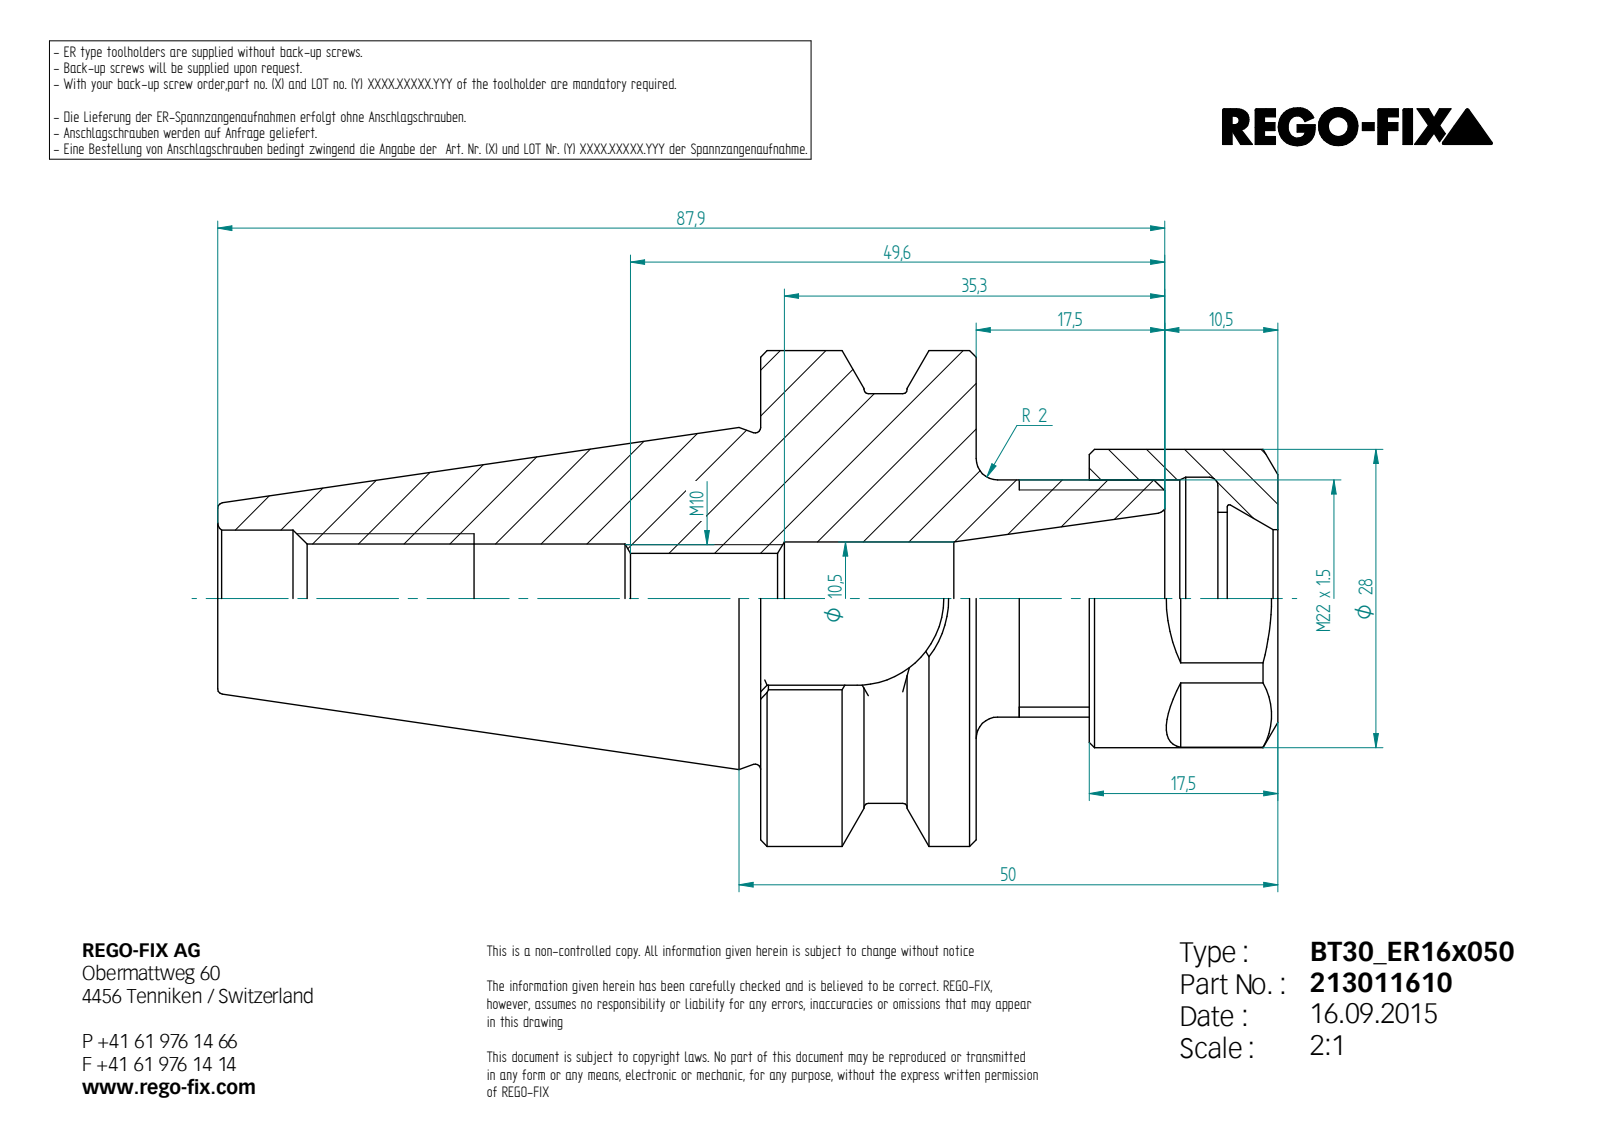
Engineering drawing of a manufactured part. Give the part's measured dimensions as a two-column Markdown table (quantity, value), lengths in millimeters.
| quantity | value |
| --- | --- |
| part name | NOCUT |
| STEP written by | SIEMENS PLM Software Solid Edge ST10 (AUTOMOTIVE_DESIGN) |
| units | millimeters |
| bodies | 2 solids, 167 faces (62 planar, 43 cylindrical, 62 other) |
| overall size | 88.3 × 46.3 × 46.3 |
| volume | 104 705 mm³ |
| surface area | 27 946 mm² |
| round holes (diameter × count) | 8.38 × 1, 10.11 × 1, 10.5 × 1, 12.2 × 1, 12.7 × 1 |
| round bosses / shafts (diameter × count) | 46.3 × 1, 46 × 1, 22.3 × 1, 22 × 1 |
| partial cylindrical surfaces (radius × count) | 0.5 × 8, 8.05 × 1, 19 × 1 |
| main face-to-face distances | 20.2, 20, 32.5, 17.5, 88.1, 70.6, 16.1, 17.7, 37.7, 17.3 |
